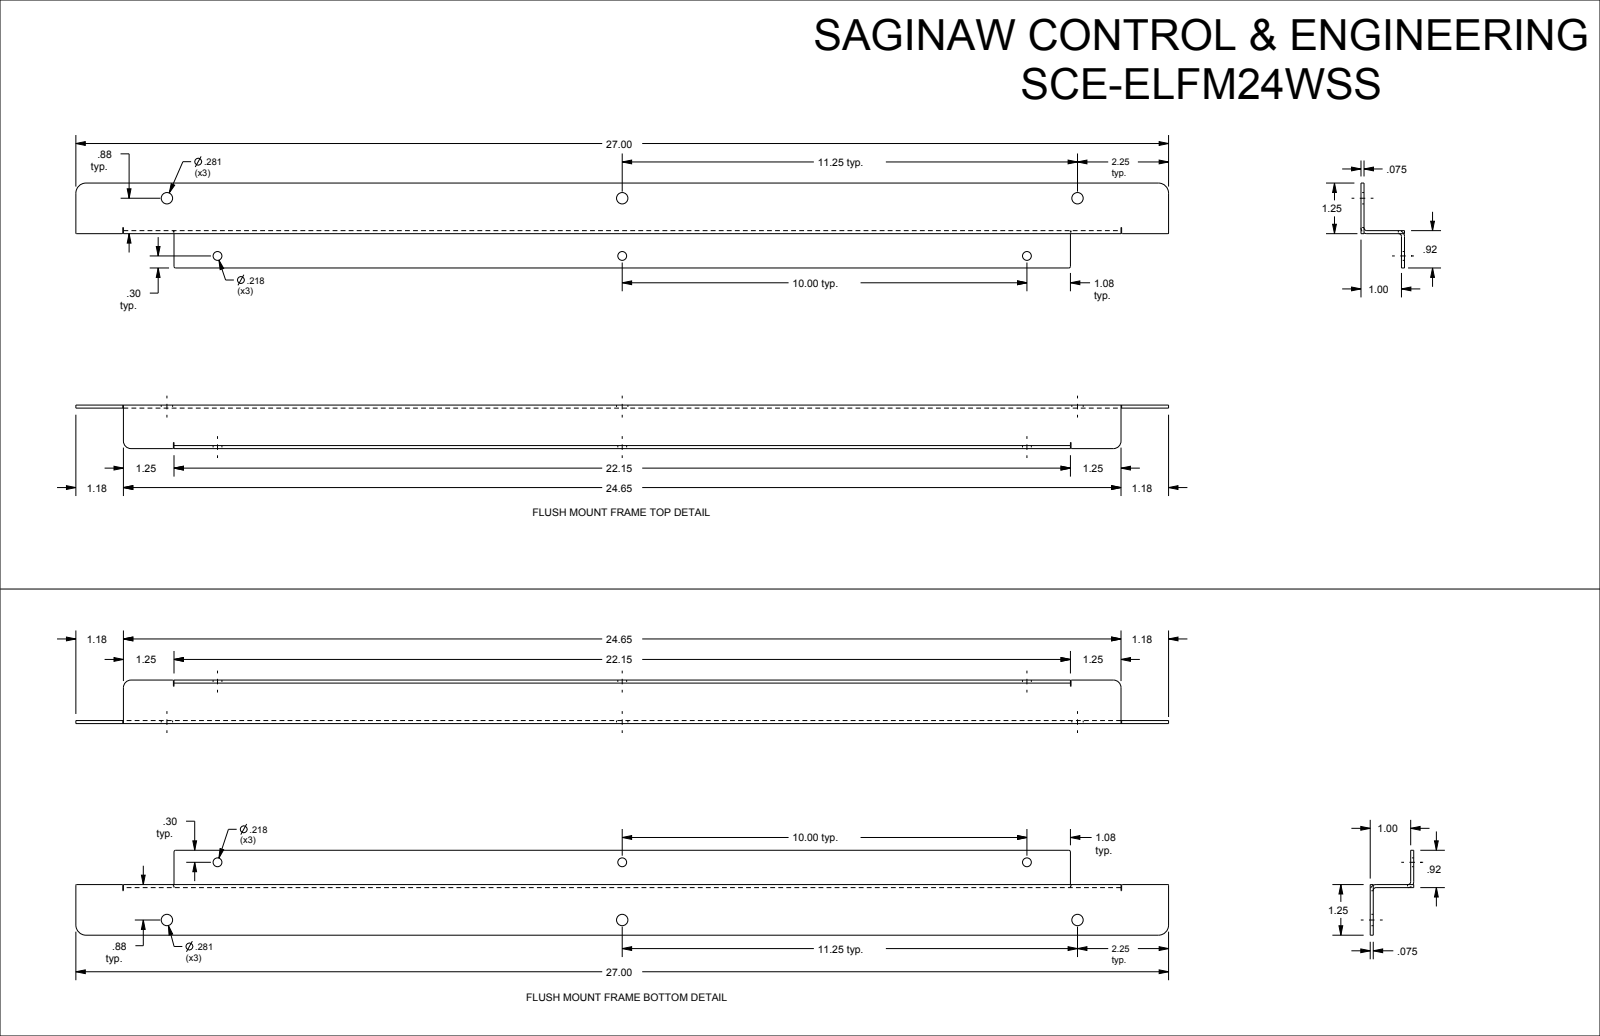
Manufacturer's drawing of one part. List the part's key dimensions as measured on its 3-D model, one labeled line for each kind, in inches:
Part name (STEP PRODUCT): SCE-ELFM24W
STEP written by: SolidWorks 2019 (CONFIG_CONTROL_DESIGN)
Units: inches
Bodies: 2 solids, 96 faces (44 planar, 52 cylindrical, 0 other)
Overall size (bounding box): 27 × 26.35 × 1.075
Volume: 11.26 in³ · Surface area: 309.9 in²
Round holes (diameter × count): ⌀0.218 ×6, ⌀0.281 ×6
Partial cylindrical surfaces — rounded edges, fillets, slot ends (radius × count): R0.015 ×10, R0.007 ×6, R0.04 ×4, R0.051 ×4, R0.126 ×4, R0.25 ×4, R0.187 ×2
Main face-to-face distances: 0.075, 1, 0.075, 23.925, 1.075, 0.925, 23.85, 24, 0.922, 23.078
Hole centre spacings: 10, 10.101, 11.25, 11.34, 21.298, 24.851, 27.963, 22.75
